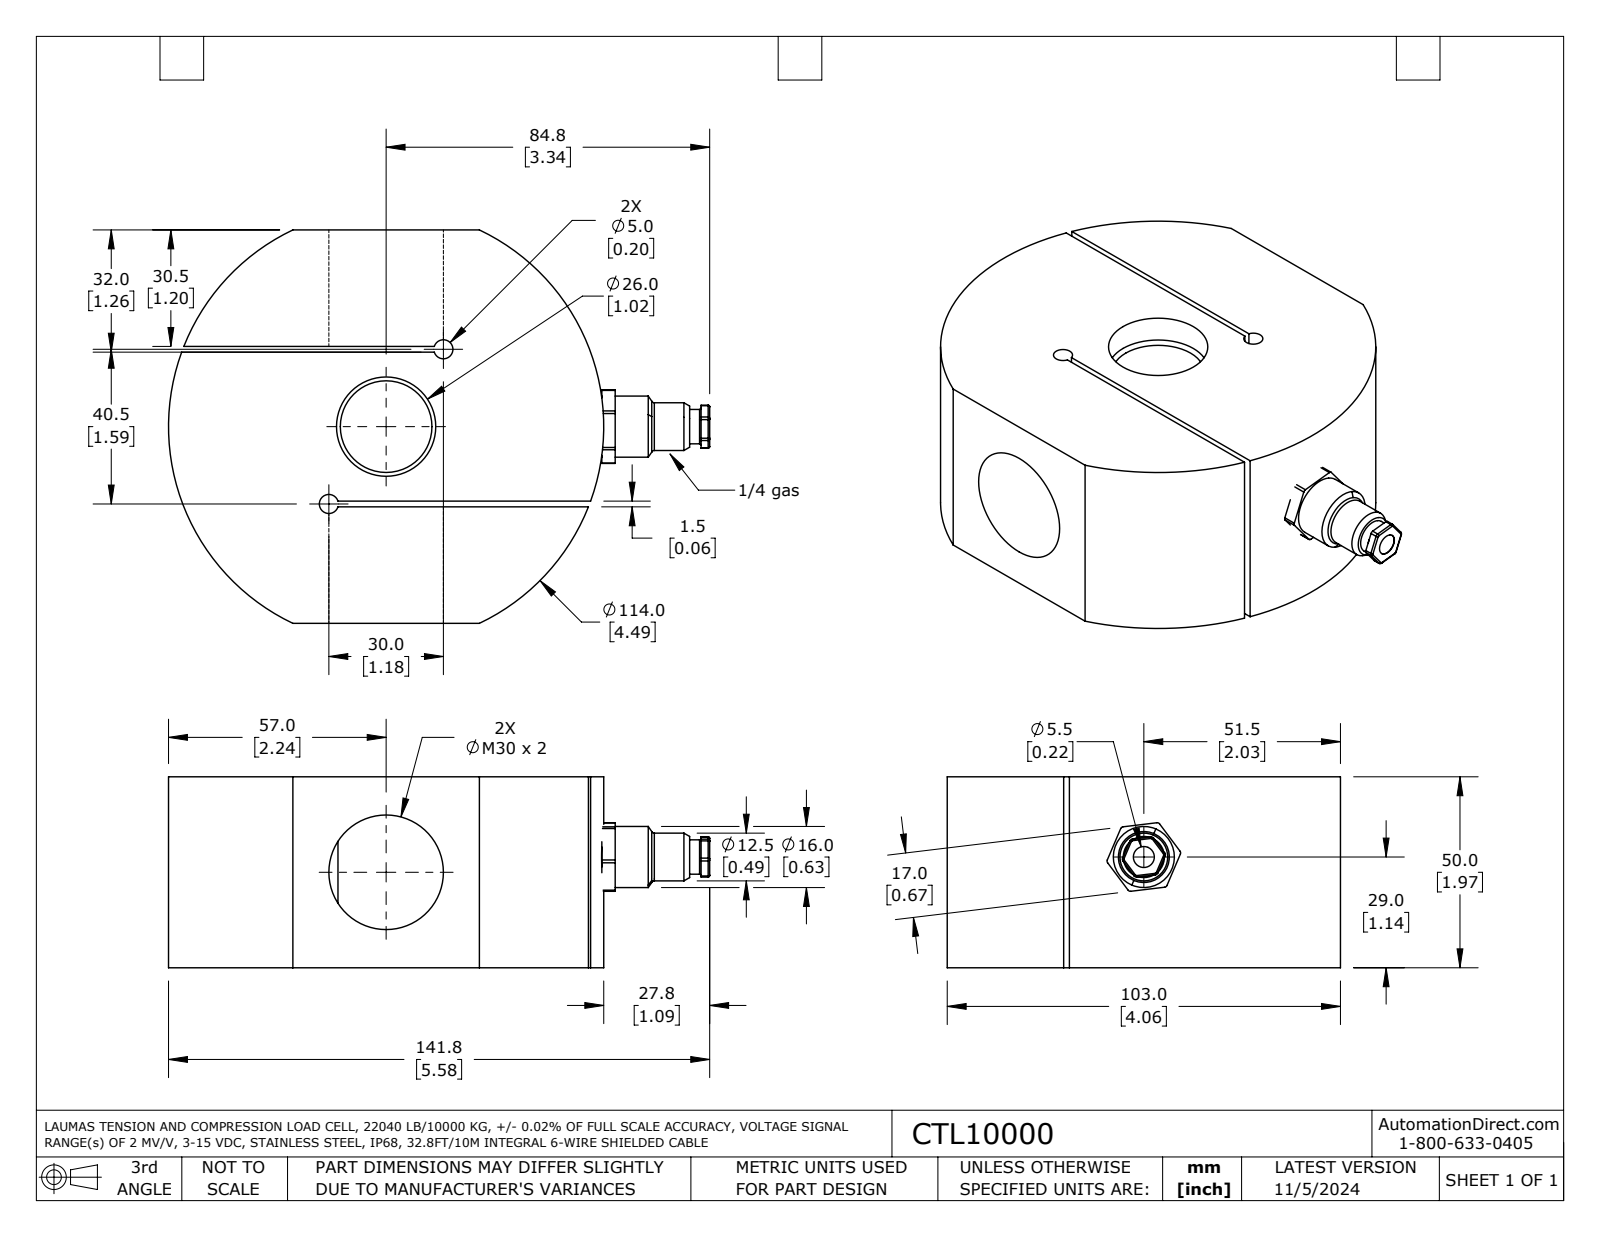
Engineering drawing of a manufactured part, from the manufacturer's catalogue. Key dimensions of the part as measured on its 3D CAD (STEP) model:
Part name (STEP PRODUCT): CTL10000
STEP written by: SolidWorks 2021 (AUTOMOTIVE_DESIGN)
Units: inches
Bodies: 2 solids, 100 faces (31 planar, 50 cylindrical, 19 other)
Overall size (bounding box): 5.581 × 4.055 × 1.969
Volume: 26.32 in³ · Surface area: 89.55 in²
Round holes (diameter × count): ⌀0.197 ×2, ⌀0.217 ×1, ⌀0.551 ×1, ⌀1.024 ×1, ⌀1.181 ×1
Round bosses / shafts (diameter × count): ⌀0.63 ×1, ⌀0.492 ×1, ⌀0.354 ×1
Partial cylindrical surfaces — rounded edges, fillets, slot ends (radius × count): R0.03 ×12, R0.016 ×6, R2.244 ×1
Main face-to-face distances: 1.969, 0.059, 1.594, 1.654, 1.201, 1.26, 2.795, 2.854, 1.535, 4.055
Hole centre spacings: 0.992, 1.984
